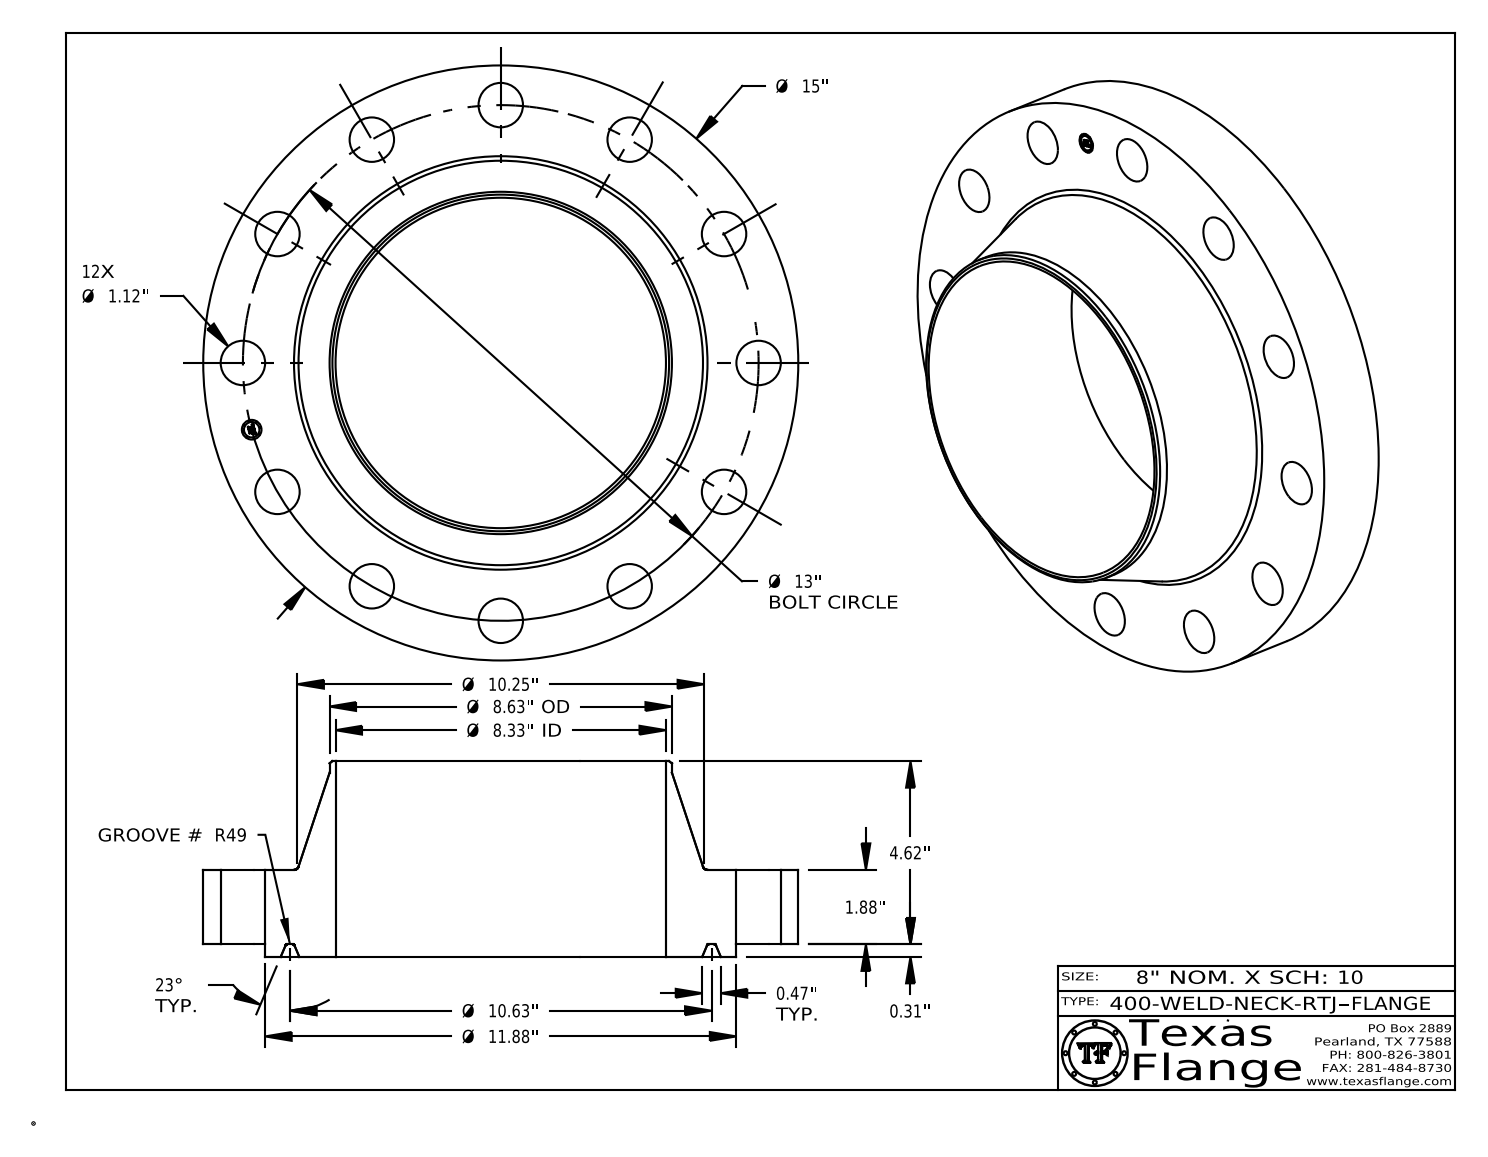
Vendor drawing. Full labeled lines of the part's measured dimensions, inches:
Part name (STEP PRODUCT): 400-WELD-NECK-RTJ
STEP written by: CATIA V5 STEP AP214 (AUTOMOTIVE_DESIGN)
Units: inches
Bodies: 1 solid, 437 faces (371 planar, 52 cylindrical, 14 other)
Overall size (bounding box): 15 × 15 × 4.933
Volume: 261.2 in³ · Surface area: 601.8 in²
Round holes (diameter × count): ⌀1.12 ×12, ⌀0.495 ×1, ⌀8.329 ×1
Round bosses / shafts (diameter × count): ⌀0.03 ×8, ⌀15 ×1, ⌀11.875 ×1, ⌀8.63 ×1, ⌀0.39 ×1
Main face-to-face distances: 1.88, 0.313, 2.193, 4.933, 4.62, 2.74, 2.178, 1.865, 0.015, 2.755
Hole centre spacings: 6.5, 3.365, 9.193, 11.258, 12.557, 13, 1.697, 4.975
